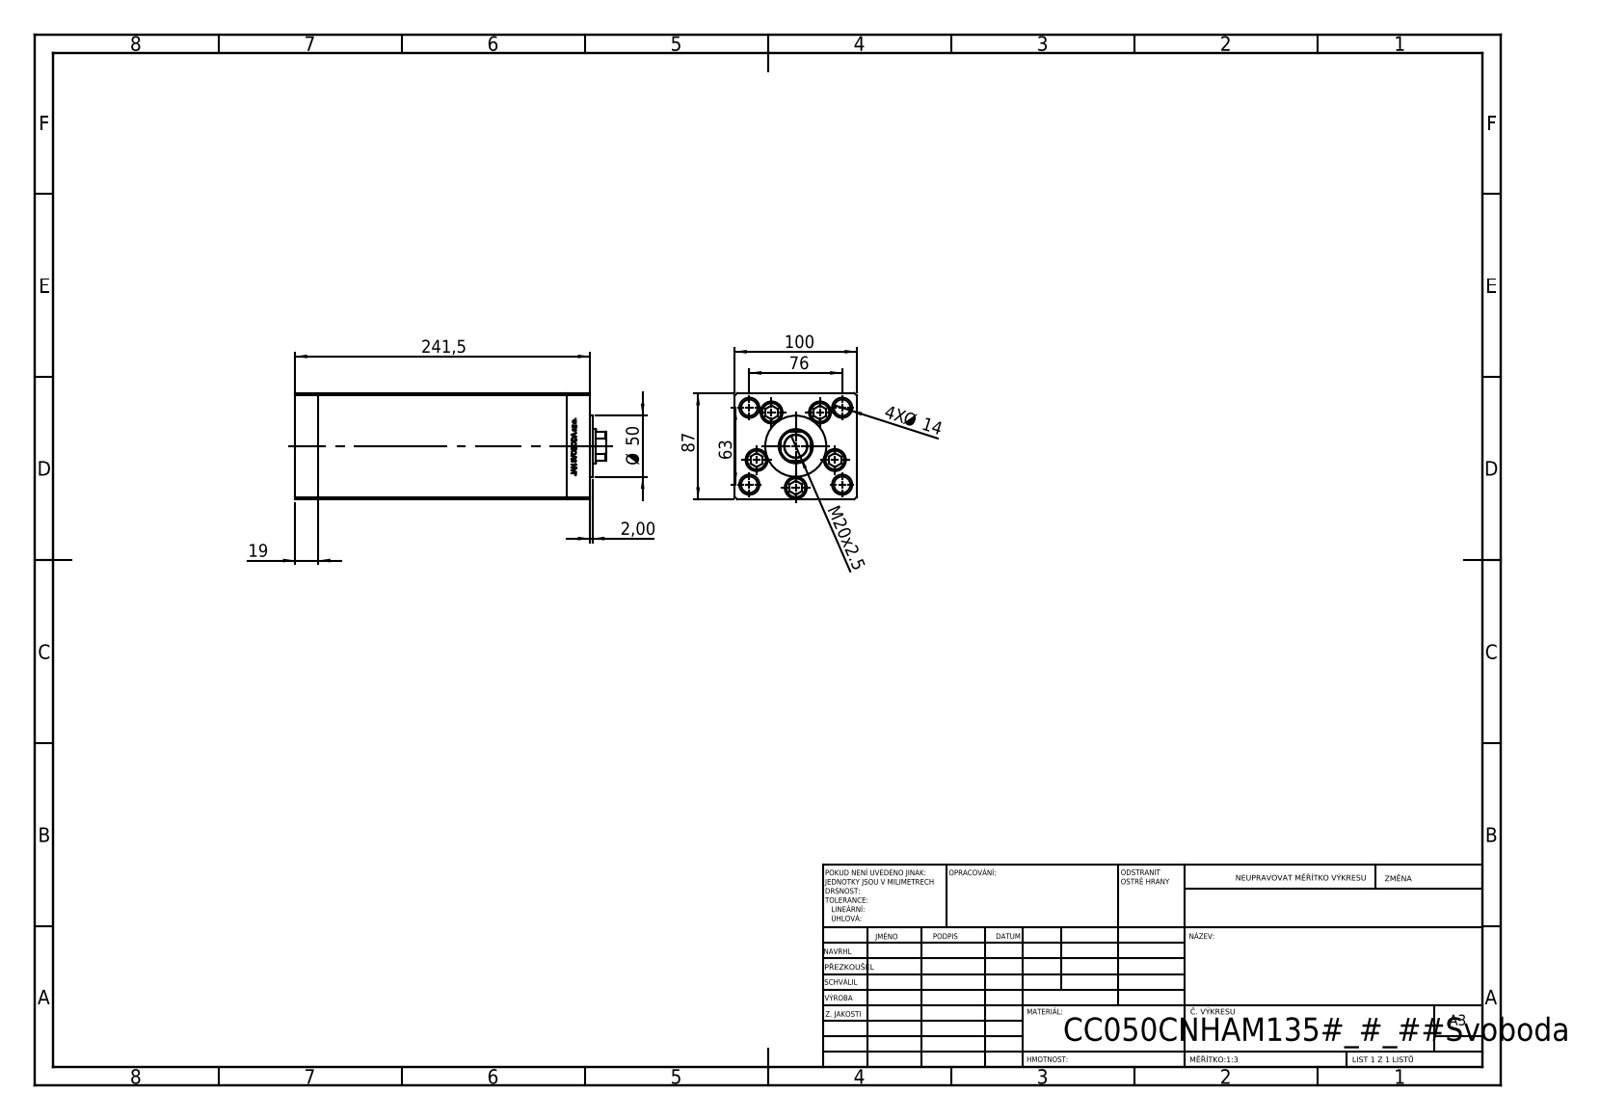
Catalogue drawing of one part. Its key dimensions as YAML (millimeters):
part_name: "ALLEN BOLT; V220C FRONT; V220C_C MIDDLE; V220C_VC_C (+1 more)"
step_written_by: "SolidWorks 2019 (CONFIG_CONTROL_DESIGN)"
units: millimeters
bodies: {solids: 13, faces: 1186, planar: 548, cylindrical: 176, other: 462}
overall_size: [254.5, 100, 87]
volume: 1713000
surface_area: 269893
round_holes:
  - {diameter: 13.5, count: 9}
  - {diameter: 18, count: 5}
  - {diameter: 2, count: 4}
  - {diameter: 12, count: 4}
  - {diameter: 13.16, count: 4}
  - {diameter: 16.5, count: 4}
  - {diameter: 17, count: 1}
  - {diameter: 18.5, count: 1}
  - {diameter: 28, count: 1}
round_bosses_or_shafts:
  - {diameter: 8, count: 5}
  - {diameter: 17, count: 4}
  - {diameter: 50, count: 1}
partial_cylinders:
  - {radius: 0.93, count: 2}
  - {radius: 13.5, count: 1}
face_to_face_distances: [100, 87, 19, 203.5, 222.5, 34.25, 241.5, 207.25, 188.25, 15.25]
hole_center_spacings: [34, 49.36, 18.59, 21.03, 38.08, 39.27, 40.83, 43.24]
